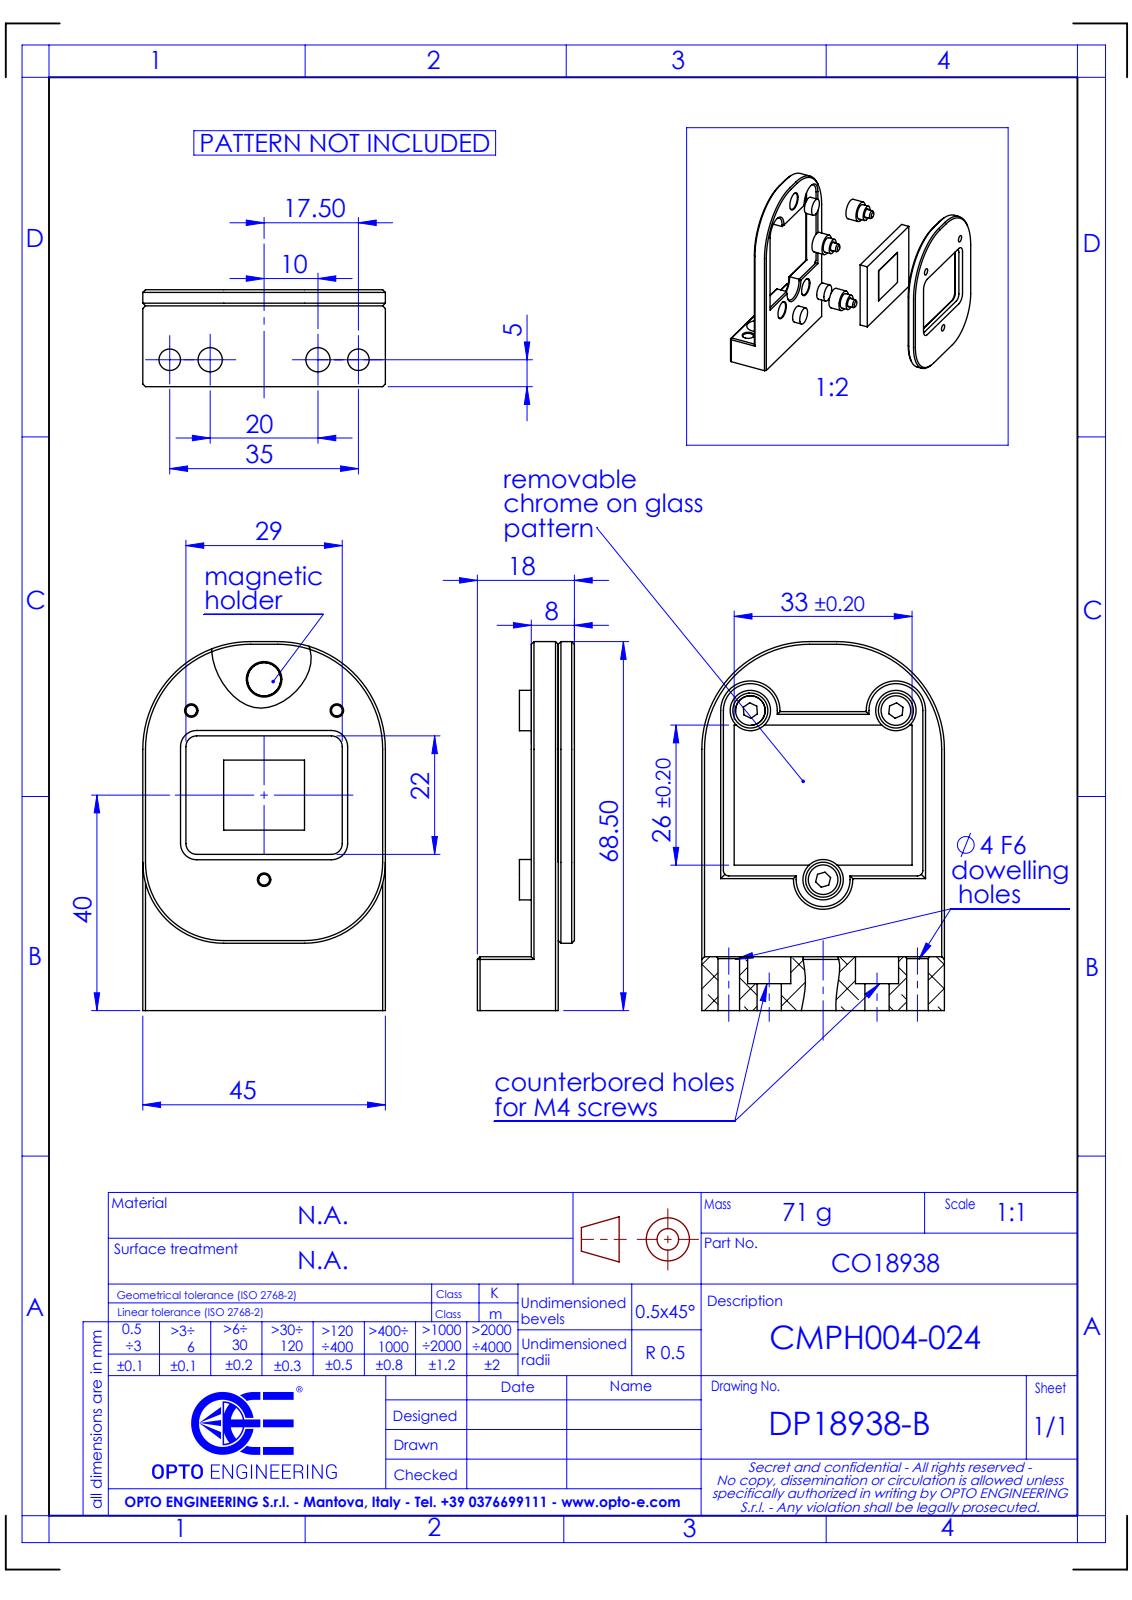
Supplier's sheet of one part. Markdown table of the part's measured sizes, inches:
| quantity | value |
| --- | --- |
| part name | DP18936-B_CMPH004-024 |
| STEP written by | SolidWorks 2021 (CONFIG_CONTROL_DESIGN) |
| units | inches |
| bodies | 0 solids, 190 faces (96 planar, 51 cylindrical, 43 other) |
| overall size | 2.697 × 1.772 × 0.709 |
| round holes (diameter × count) | 0.098 × 3, 0.157 × 2, 0.177 × 2, 0.315 × 2 |
| round bosses / shafts (diameter × count) | 0.295 × 3, 0.217 × 3 |
| partial cylindrical surfaces (radius × count) | 0.079 × 4, 0.197 × 3, 0.039 × 2, 0.591 × 2, 0.787 × 2 |
| main face-to-face distances | 0.118, 0.197, 0.315, 0.394, 0.591, 0.709, 0.157, 1.772, 1.614, 1.457 |
| hole center spacings | 0.295, 1.083, 1.346, 0.787, 1.063, 1.378 |
